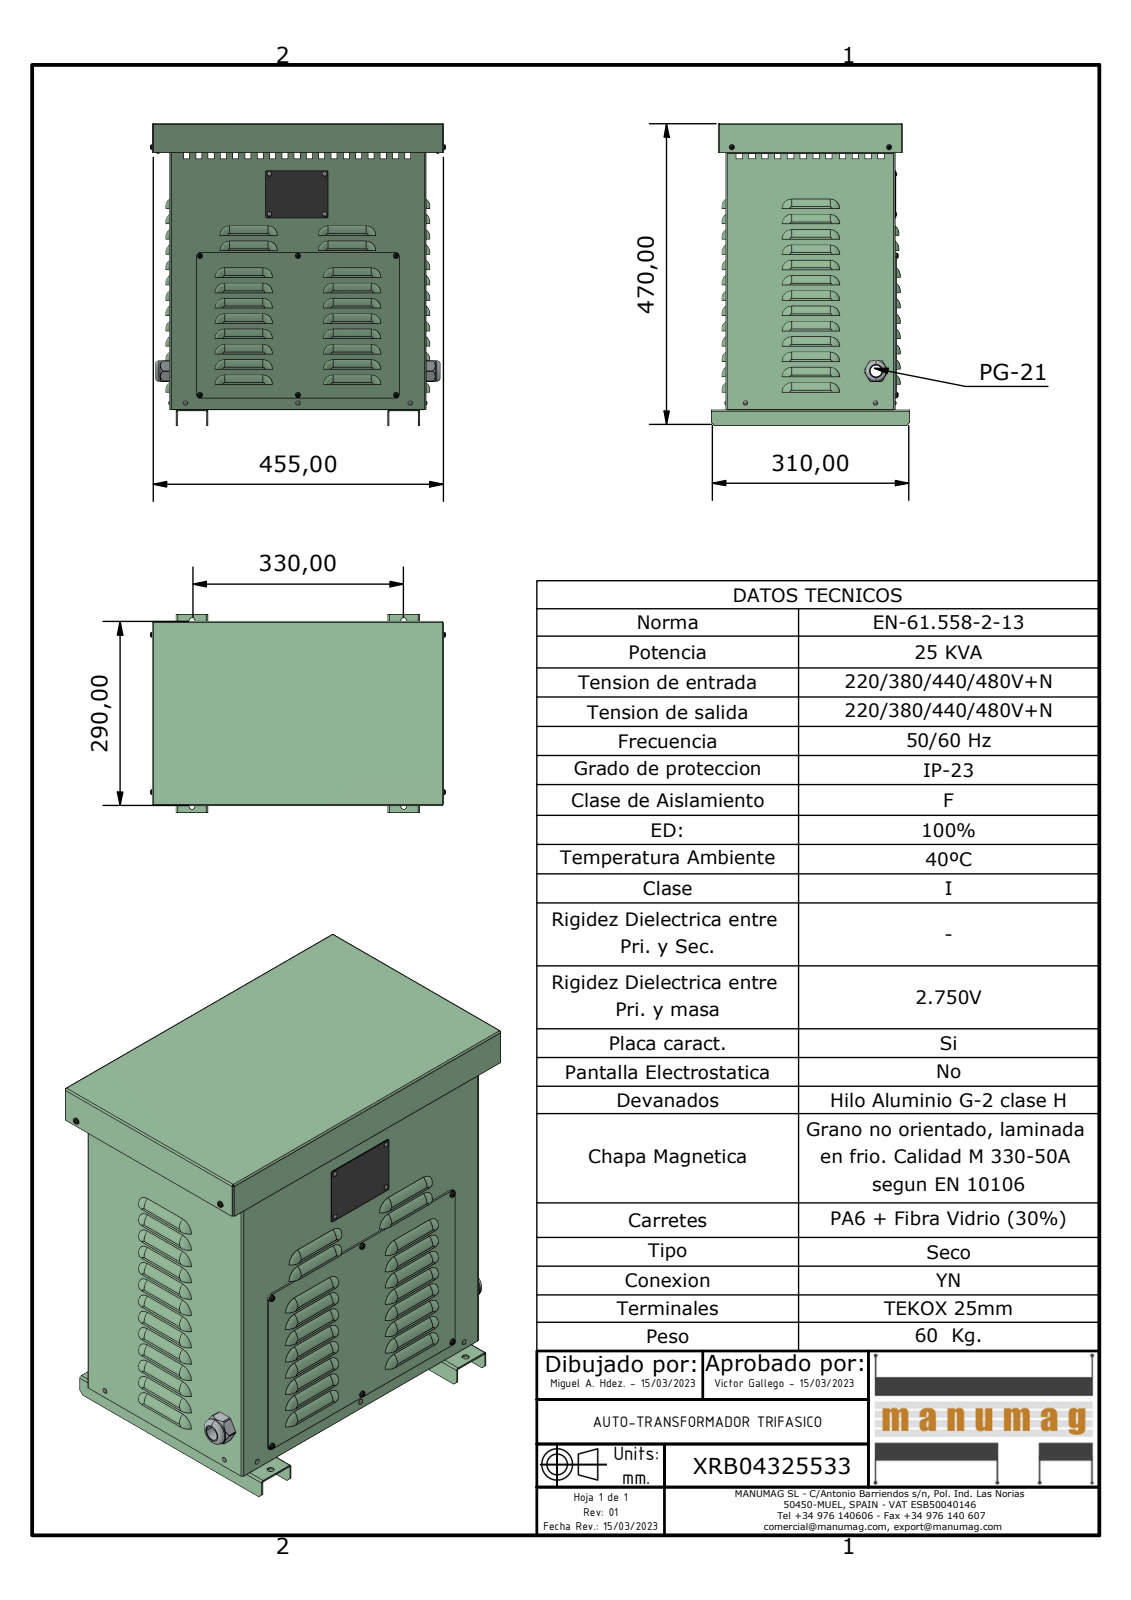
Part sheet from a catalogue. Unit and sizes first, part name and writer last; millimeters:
Units: millimetres
Overall size (bounding box): 474.44 × 463.69 × 310
Round holes (diameter × count): ⌀3.4 ×17, ⌀4 ×9, ⌀2.3 ×8, ⌀9 ×6, ⌀5.1 ×3, ⌀8.92 ×2, ⌀18 ×1, ⌀29.9 ×1
Round bosses / shafts (diameter × count): ⌀3.2 ×9, ⌀4 ×8, ⌀3.62 ×8, ⌀32.4 ×1, ⌀28.5 ×1, ⌀28.3 ×1
Partial cylindrical surfaces — rounded edges, fillets, slot ends (radius × count): R14 ×118, R4 ×63, R15 ×49, R2 ×10, R2 ×9, R3.47 ×8, R0.5 ×6, R2.5 ×6
Main face-to-face distances: 2, 262.92, 264.92, 400.8, 447.27, 449.27, 260.92, 398.8, 402.8, 4
Hole centre spacings: 218.1, 153.8, 154.1, 266.87, 267.05, 307.9, 332.28, 377.32
Volume: 2 342 000 mm³ · Surface area: 2 098 000 mm²
Bodies: 33 solids, 2242 faces (1225 planar, 489 cylindrical, 528 other)
Part name (STEP PRODUCT): XRB04325533; JE015 - JE020 - JE025 EXPORT CUERPO; JE015 - JE020 - JE025 EXPORT BASE; JE015 - JE020 - JE025 EXPORT PATA (+6 more)
STEP written by: Autodesk Inventor 2023 (AUTOMOTIVE_DESIGN)
